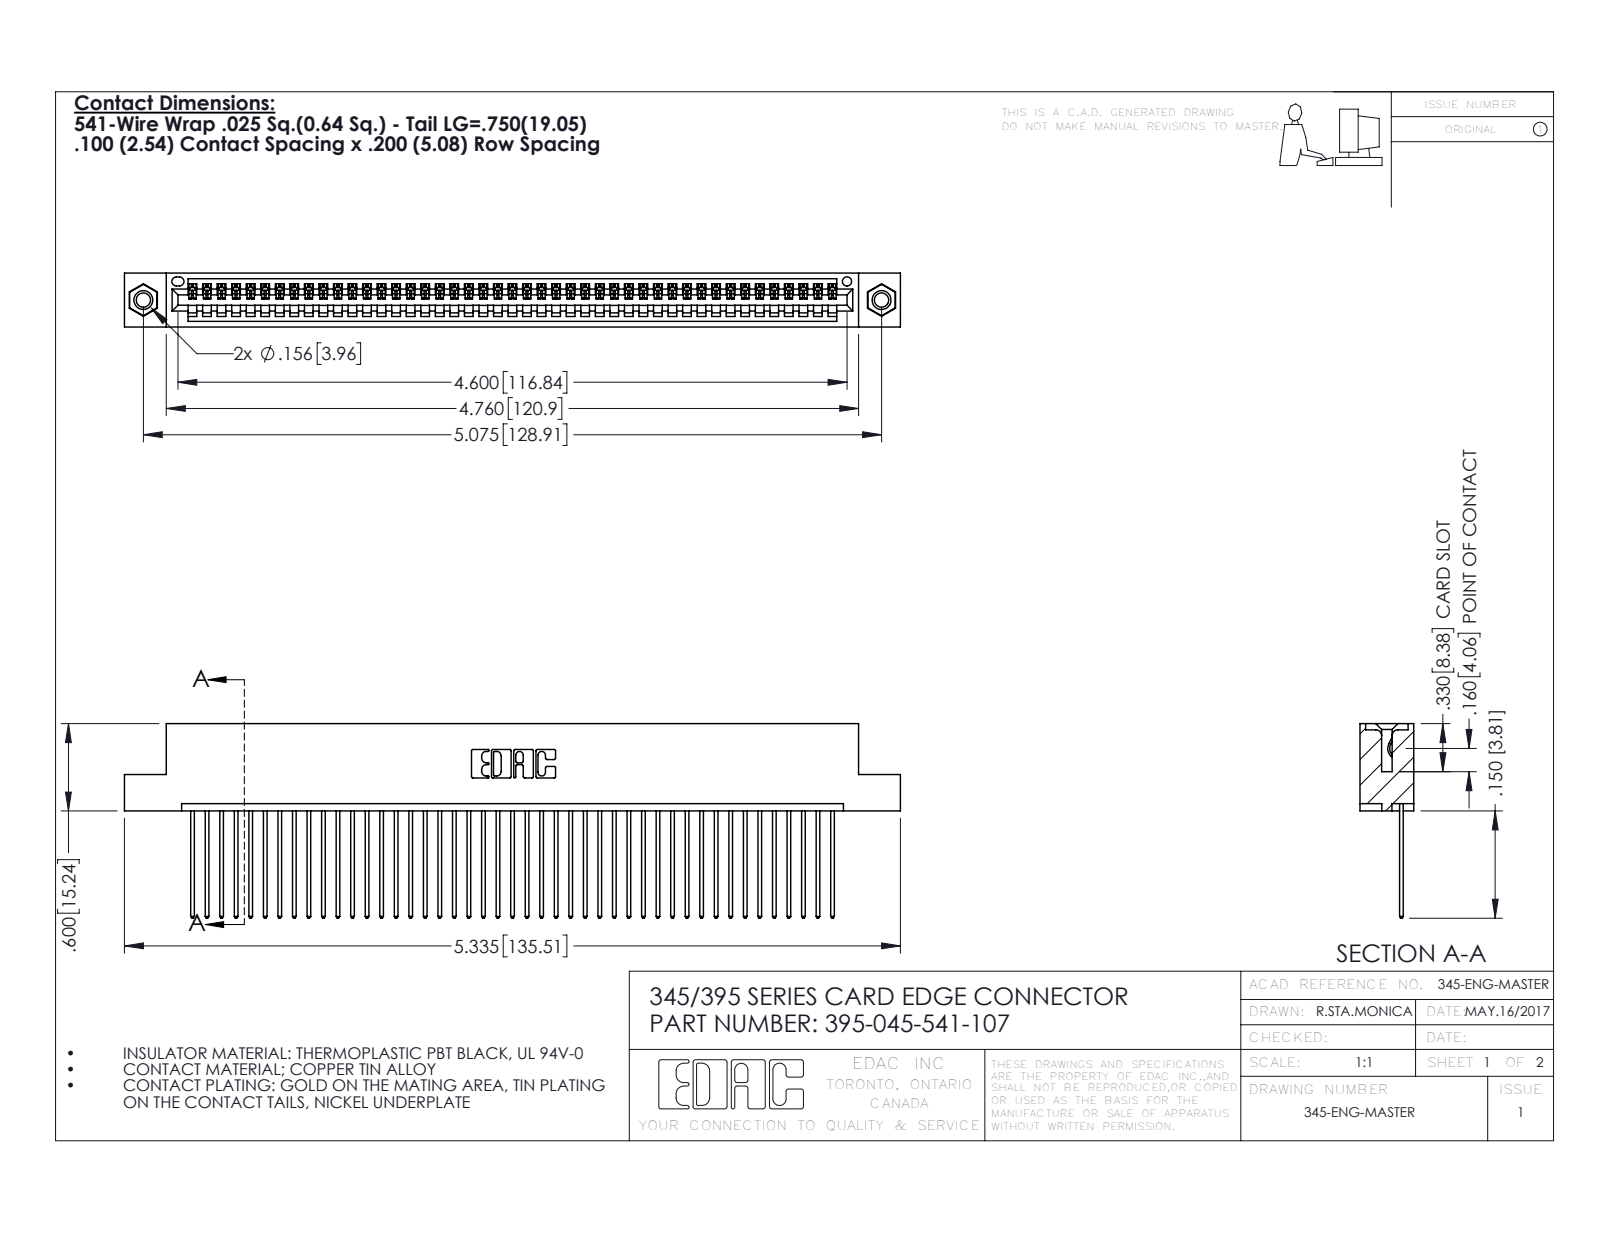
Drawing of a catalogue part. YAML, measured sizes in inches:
part_name: "345 Part_Flush Mounting Lugs - 0.156 Dia-TI; 345-292-001_345-293-141; 345-250-001_345-250-005-103; 395-045-541-107"
step_written_by: "SolidWorks 2016 (CONFIG_CONTROL_DESIGN)"
units: inches
bodies: {solids: 48, faces: 2796, planar: 1912, cylindrical: 868, other: 16}
overall_size: [5.335, 1.337, 0.37]
volume: 0.795
surface_area: 28.31
round_holes:
  - {diameter: 0.098, count: 2}
  - {diameter: 0.125, count: 2}
  - {diameter: 0.156, count: 2}
  - {diameter: 0.064, count: 1}
round_bosses_or_shafts:
  - {diameter: 0.155, count: 2}
partial_cylinders:
  - {radius: 0.006, count: 90}
  - {radius: 0.01, count: 90}
  - {radius: 0.01, count: 22}
  - {radius: 0.007, count: 6}
  - {radius: 0.031, count: 6}
  - {radius: 0.026, count: 3}
  - {radius: 0.031, count: 2}
  - {radius: 0.04, count: 2}
face_to_face_distances: [0.072, 0.298, 0.098, 0.272, 0.025, 0.37, 0.2, 0.225, 0.149, 0.072]
hole_center_spacings: [0.27, 4.839, 5.075]
